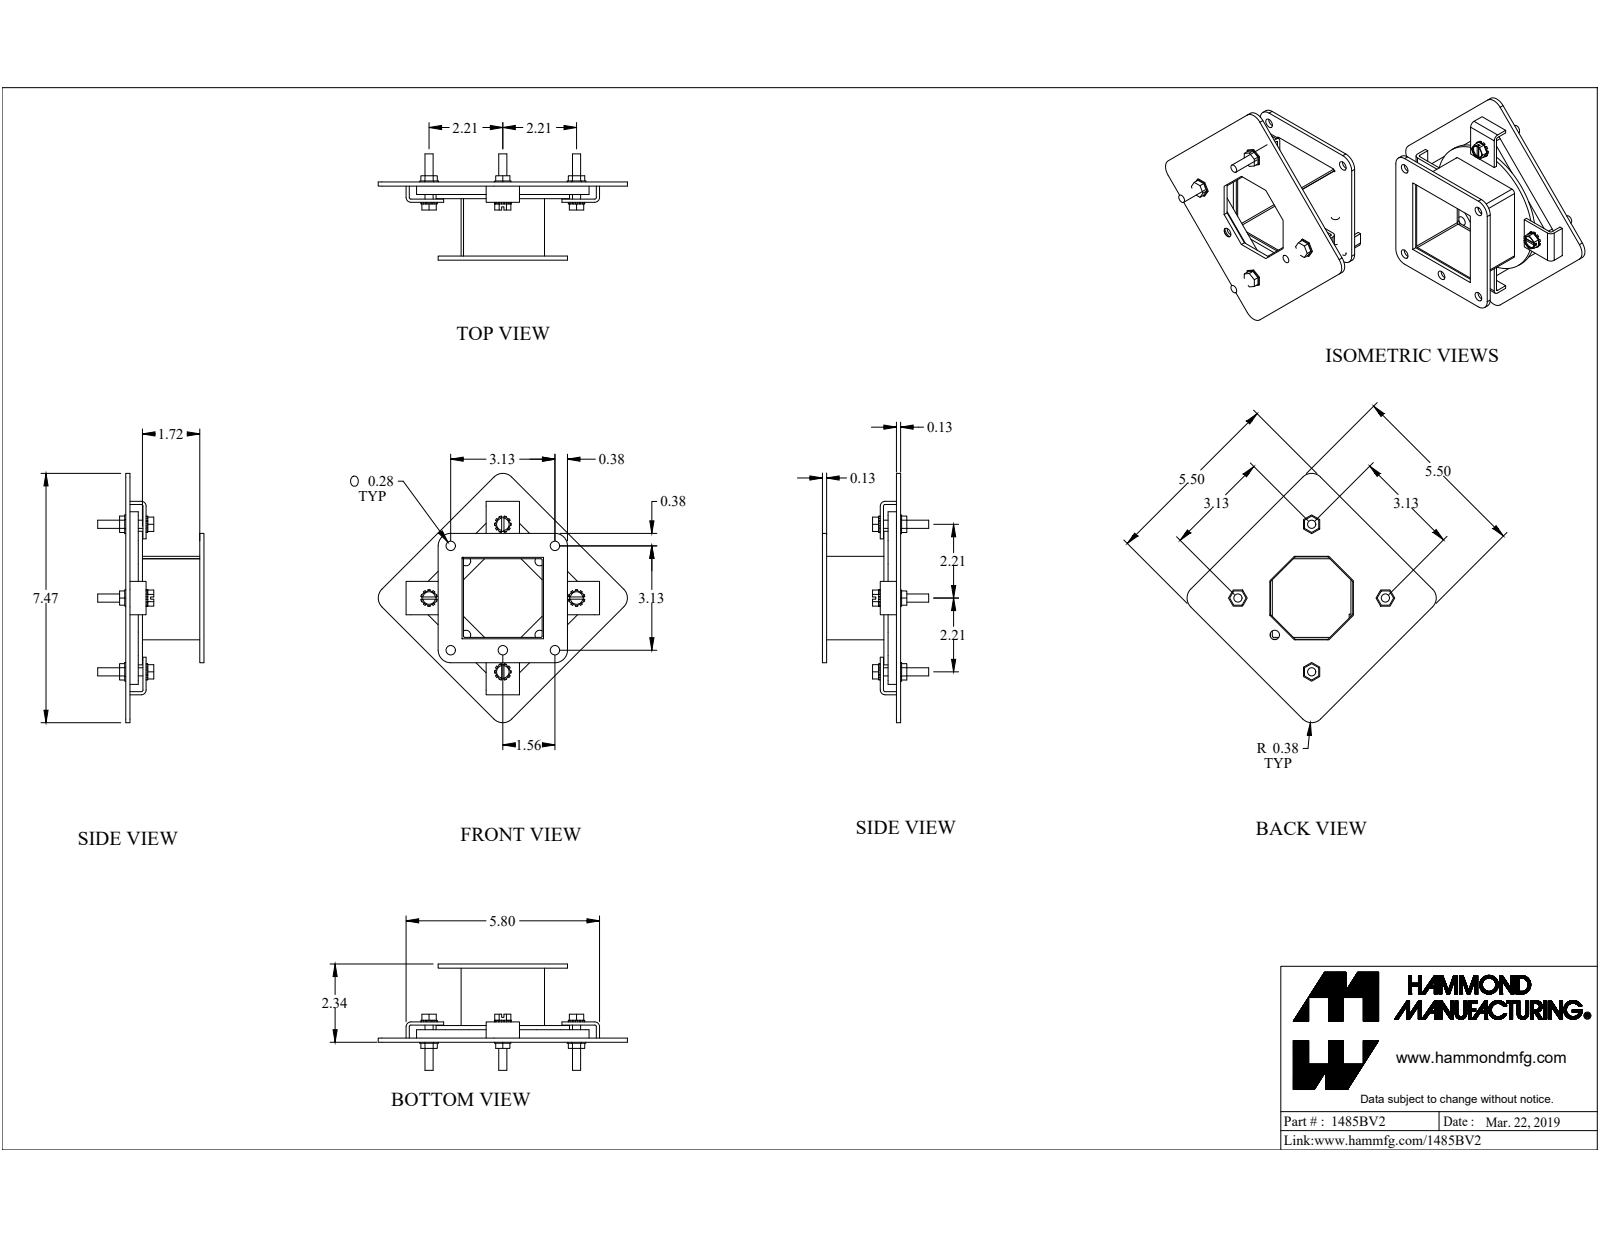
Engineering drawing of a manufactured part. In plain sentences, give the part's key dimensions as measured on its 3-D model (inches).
The part is named "1485BV2". Its 3-D file was written by "SolidWorks 2019 (CONFIG_CONTROL_DESIGN)". It is 31 solids with 624 faces: 437 planar, 175 cylindrical and 12 other. Overall it measures 7.468 by 7.468 by 3.434 inches. Its volume is 14.55 cubic inches and its surface area 246 square inches. Round holes: 16 of diameter 0.281, 6 of diameter 0.375, 5 of diameter 0.196, 4 of diameter 0.258, 4 of diameter 0.312, 2 of diameter 0.187, 1 of diameter 0.224, 1 of diameter 0.265, 1 of diameter 0.313. Round bosses or shafts: 5 of diameter 0.244, 1 of diameter 4, 1 of diameter 0.563, 1 of diameter 0.25. Partial cylindrical surfaces (rounded edges, fillets, slot ends): 12 of radius 0.25, 12 of radius 0.375, 9 of radius 0.048, 9 of radius 0.143, 4 of radius 0.062, 3 of radius 0.036, 3 of radius 0.108, 1 of radius 0.06. The main face-to-face distances are 0.125, 0.25, 2.218, 0.375, 0.125, 2.593, 2.343, 2.093, 1.843, 0.072. The hole center spacings are 2.706, 1.563, 1.691, 4.083, 3.125, 1.196, 2.887, 3.494.
